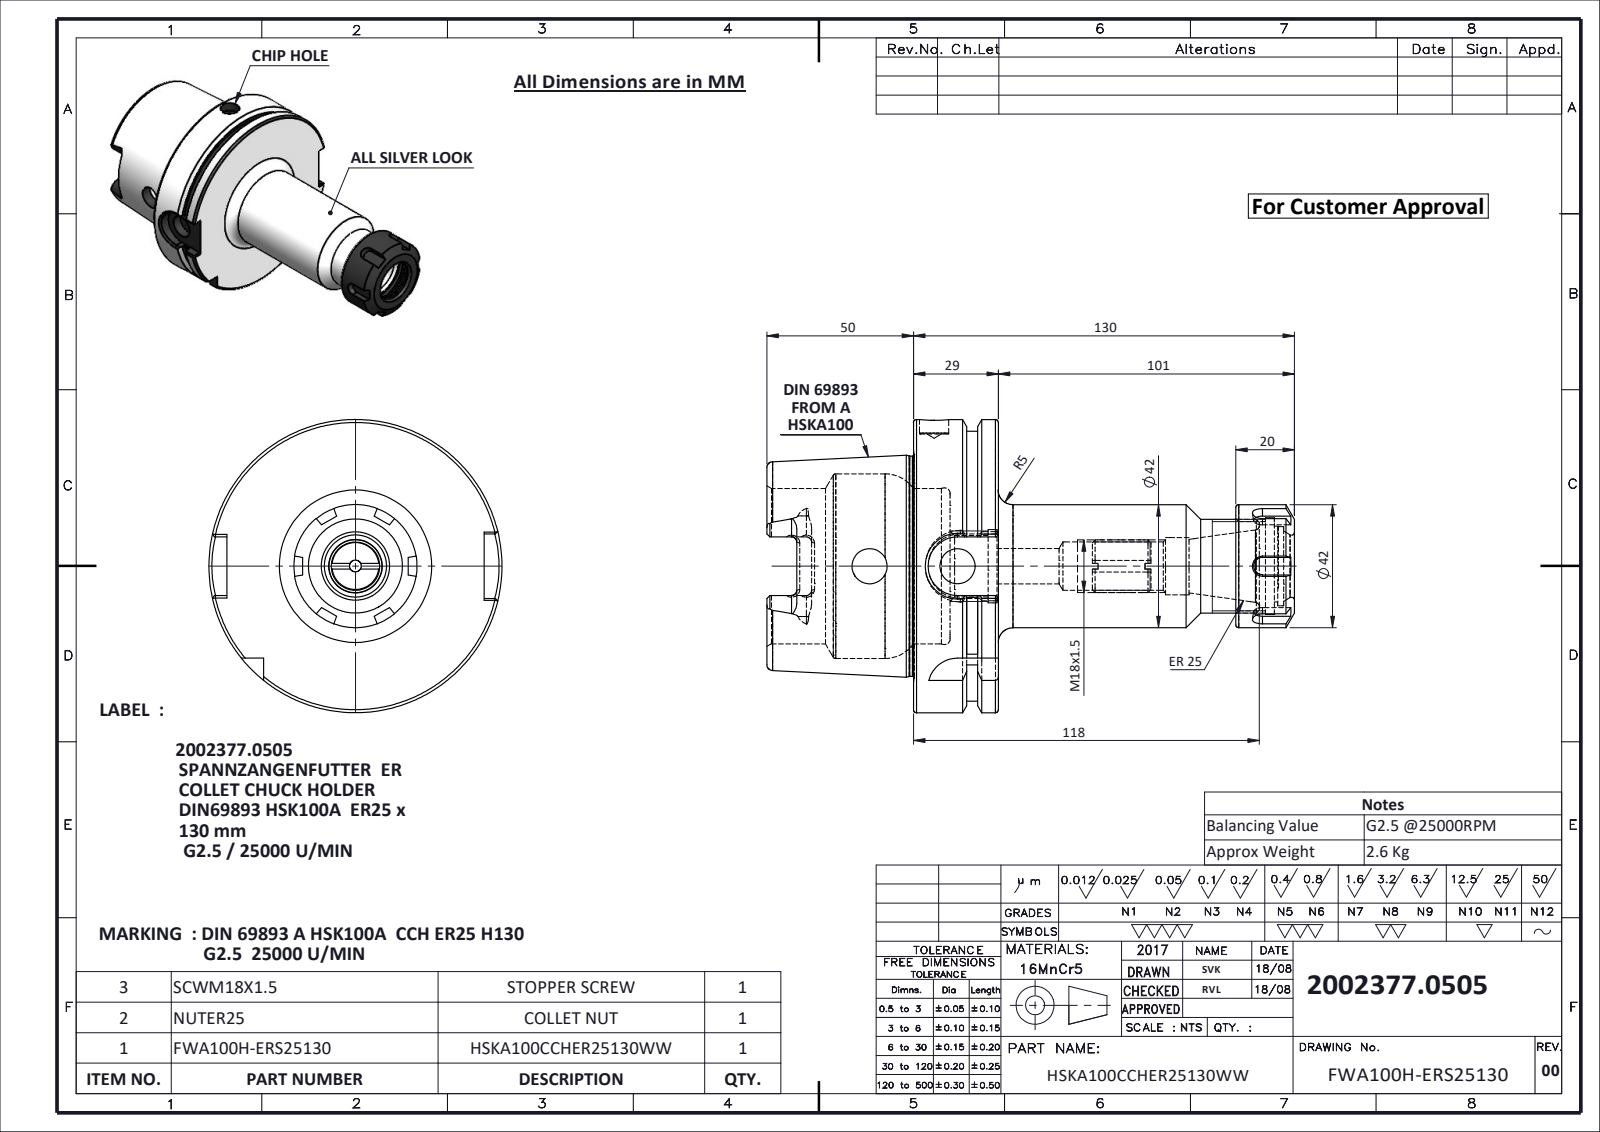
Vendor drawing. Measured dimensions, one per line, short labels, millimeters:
name: FTSCWM18X150; HSKA100CCHER25130WW; FTNUTER25; FWA100H-ERS25130
written by: SolidWorks 2024 (CONFIG_CONTROL_DESIGN)
unit: mm
bodies: 3 solids, 260 faces (94 planar, 68 cylindrical, 98 other)
size: 180 × 100 × 100
volume: 360 157 mm³; area: 73 184 mm²
holes: 3× ⌀12, 1× ⌀4, 1× ⌀10, 1× ⌀16.5, 1× ⌀19.5, 1× ⌀21, 1× ⌀25, 1× ⌀25.8, 1× ⌀27, 1× ⌀30.5, 1× ⌀33, 1× ⌀53
bosses: 1× ⌀100, 1× ⌀92, 1× ⌀75.16, 1× ⌀42, 1× ⌀32, 1× ⌀18
rounds: 6× R1.8, 4× R4.88, 2× R10, 1× R11
face distances: 28.95, 12.5, 16.45, 50, 62.5, 78.95, 20, 94.6, 160, 110
hole spacings: 1.5, 30
